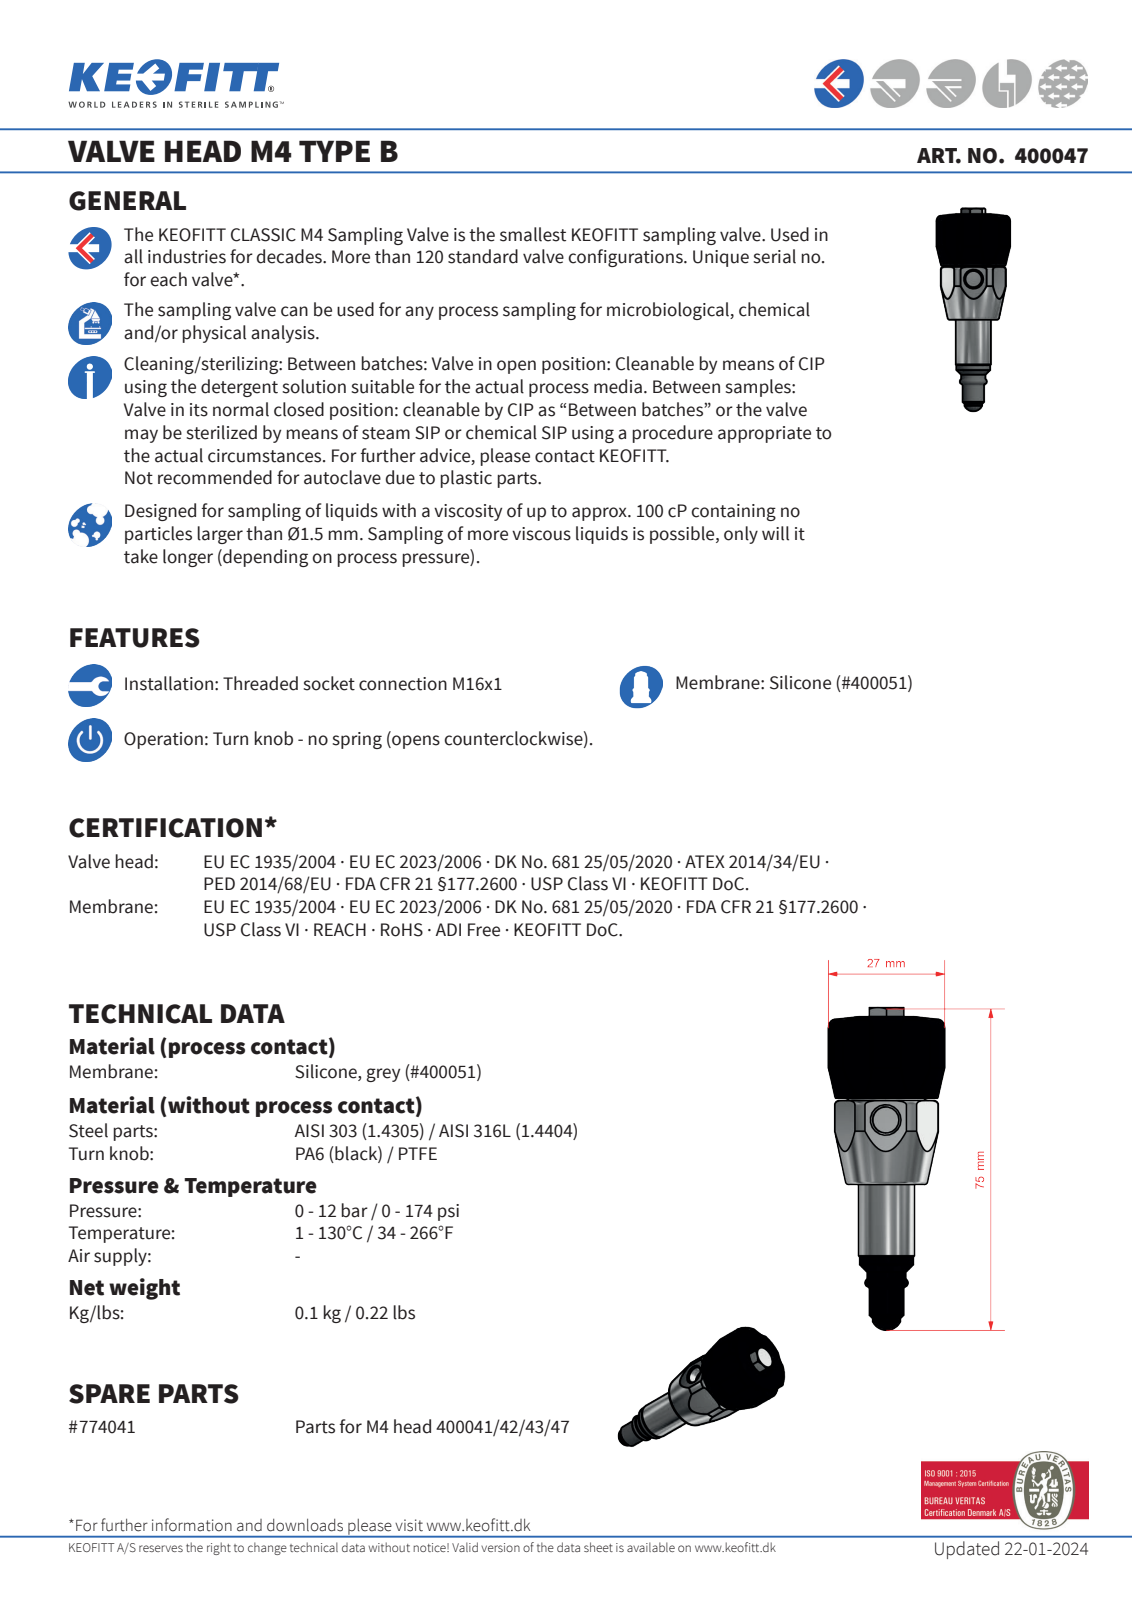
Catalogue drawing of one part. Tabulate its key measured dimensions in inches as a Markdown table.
| quantity | value |
| --- | --- |
| STEP written by | Autodesk Inventor 2008 (AUTOMOTIVE_DESIGN) |
| units | inches |
| bodies | 1 solid, 89 faces (19 planar, 30 cylindrical, 40 other) |
| overall size | 2.929 × 1.102 × 1.1 |
| volume | 1.241 in³ |
| surface area | 8.751 in² |
| round holes (diameter × count) | 0.12 × 1, 0.24 × 1, 0.492 × 1, 0.591 × 1, 0.709 × 1 |
| round bosses / shafts (diameter × count) | 0.669 × 1, 0.512 × 1, 0.354 × 1, 0.315 × 1, 0.256 × 1, 0.118 × 1 |
| partial cylindrical surfaces (radius × count) | 0.236 × 6, 0.472 × 1, 0.551 × 1 |
| main face-to-face distances | 0.866, 0.02, 0.673, 0.693, 0.867, 0.138, 0.811, 0.831, 0.315, 1.598 |
| hole center spacings | 0.039 |
